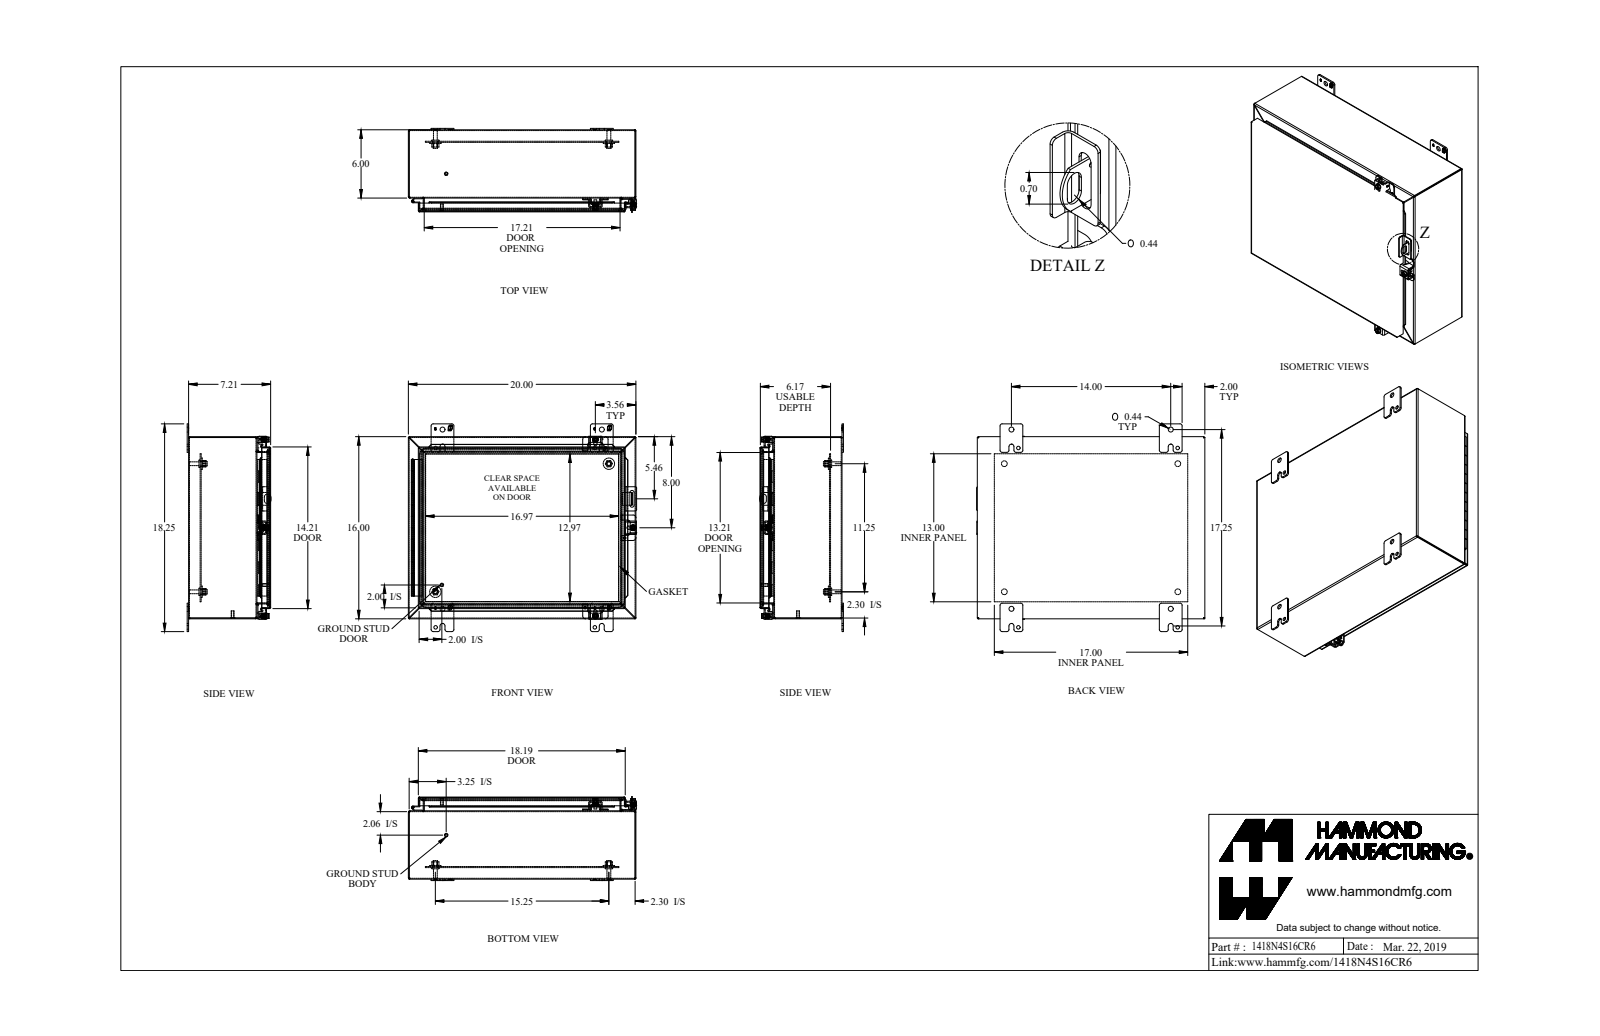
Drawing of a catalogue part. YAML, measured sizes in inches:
part_name: "1418N4S16CR6_Default"
step_written_by: "SolidWorks 2019 (CONFIG_CONTROL_DESIGN)"
units: inches
bodies: {solids: 35, faces: 1183, planar: 654, cylindrical: 401, other: 128}
overall_size: [20.063, 18.25, 7.375]
volume: 120.6
surface_area: 3186
round_holes:
  - {diameter: 0.313, count: 4}
  - {diameter: 0.437, count: 4}
  - {diameter: 0.5, count: 4}
  - {diameter: 0.213, count: 3}
  - {diameter: 0.265, count: 3}
  - {diameter: 0.375, count: 3}
  - {diameter: 0.307, count: 2}
  - {diameter: 0.445, count: 2}
  - {diameter: 0.11, count: 1}
  - {diameter: 0.125, count: 1}
round_bosses_or_shafts:
  - {diameter: 0.65, count: 4}
  - {diameter: 0.375, count: 4}
  - {diameter: 0.332, count: 4}
  - {diameter: 0.5, count: 3}
  - {diameter: 0.39, count: 3}
  - {diameter: 0.244, count: 3}
  - {diameter: 1, count: 2}
  - {diameter: 0.313, count: 2}
partial_cylinders:
  - {radius: 0.188, count: 26}
  - {radius: 0.036, count: 24}
  - {radius: 0.108, count: 24}
  - {radius: 0.25, count: 16}
  - {radius: 0.048, count: 15}
  - {radius: 0.143, count: 15}
  - {radius: 0.125, count: 10}
  - {radius: 0.045, count: 8}
face_to_face_distances: [0.072, 7.066, 7.138, 0.072, 7.138, 7.21, 0.937, 1.009, 15.928, 0.095]
hole_center_spacings: [18.951, 1.735, 14, 15.75, 21.073, 2.434, 3.064, 11.25]
